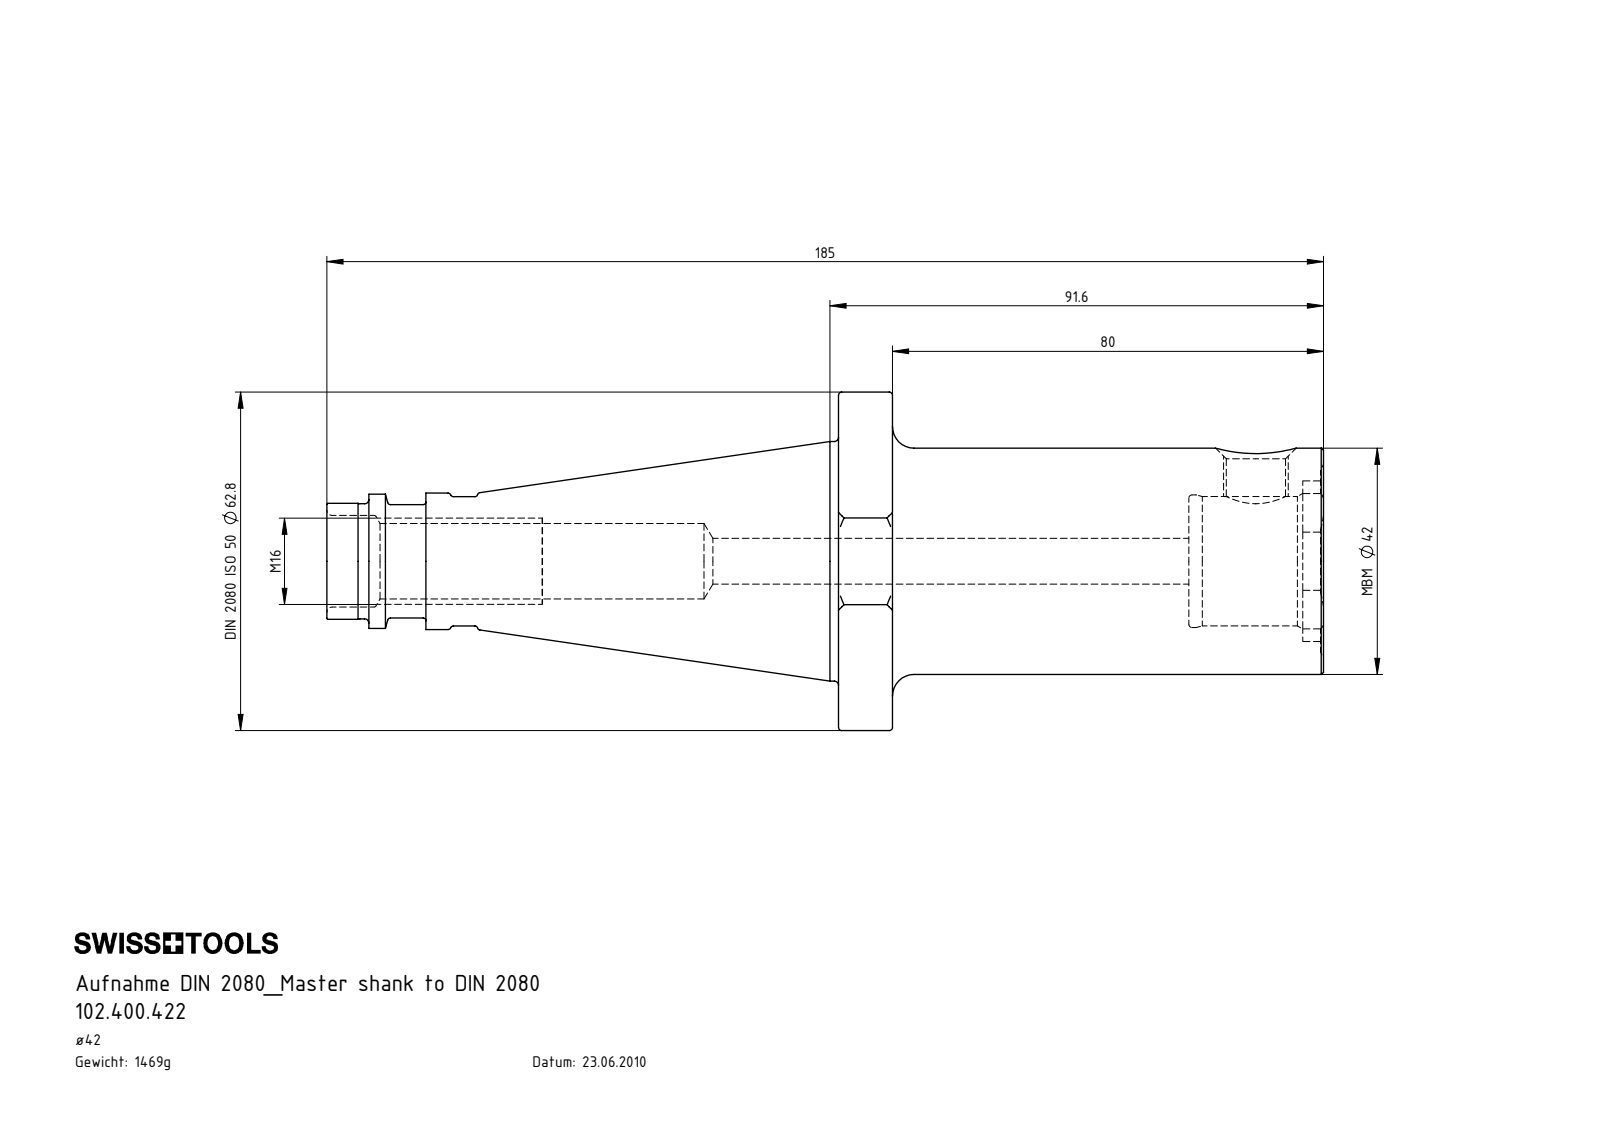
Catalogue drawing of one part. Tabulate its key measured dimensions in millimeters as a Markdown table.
| quantity | value |
| --- | --- |
| part name | 102.400.422 |
| STEP written by | SolidWorks 2017 (CONFIG_CONTROL_DESIGN) |
| units | millimeters |
| bodies | 1 solid, 148 faces (34 planar, 53 cylindrical, 61 other) |
| overall size | 185 × 62.8 × 60.7 |
| volume | 187 185 mm³ |
| surface area | 34 173 mm² |
| round holes (diameter × count) | 8.5 × 1, 11 × 1, 14 × 1, 17 × 1, 24 × 1, 24.6 × 1 |
| round bosses / shafts (diameter × count) | 62.8 × 1, 44.45 × 1, 42 × 1, 25.3 × 1, 24.91 × 1, 21.5 × 1, 21.35 × 1, 21.05 × 1 |
| partial cylindrical surfaces (radius × count) | 1.6 × 12, 5.2 × 4, 14.9 × 1, 16.52 × 1 |
| main face-to-face distances | 10, 65, 55, 86.15, 76.15, 21.15, 90, 80, 25, 3.85 |
